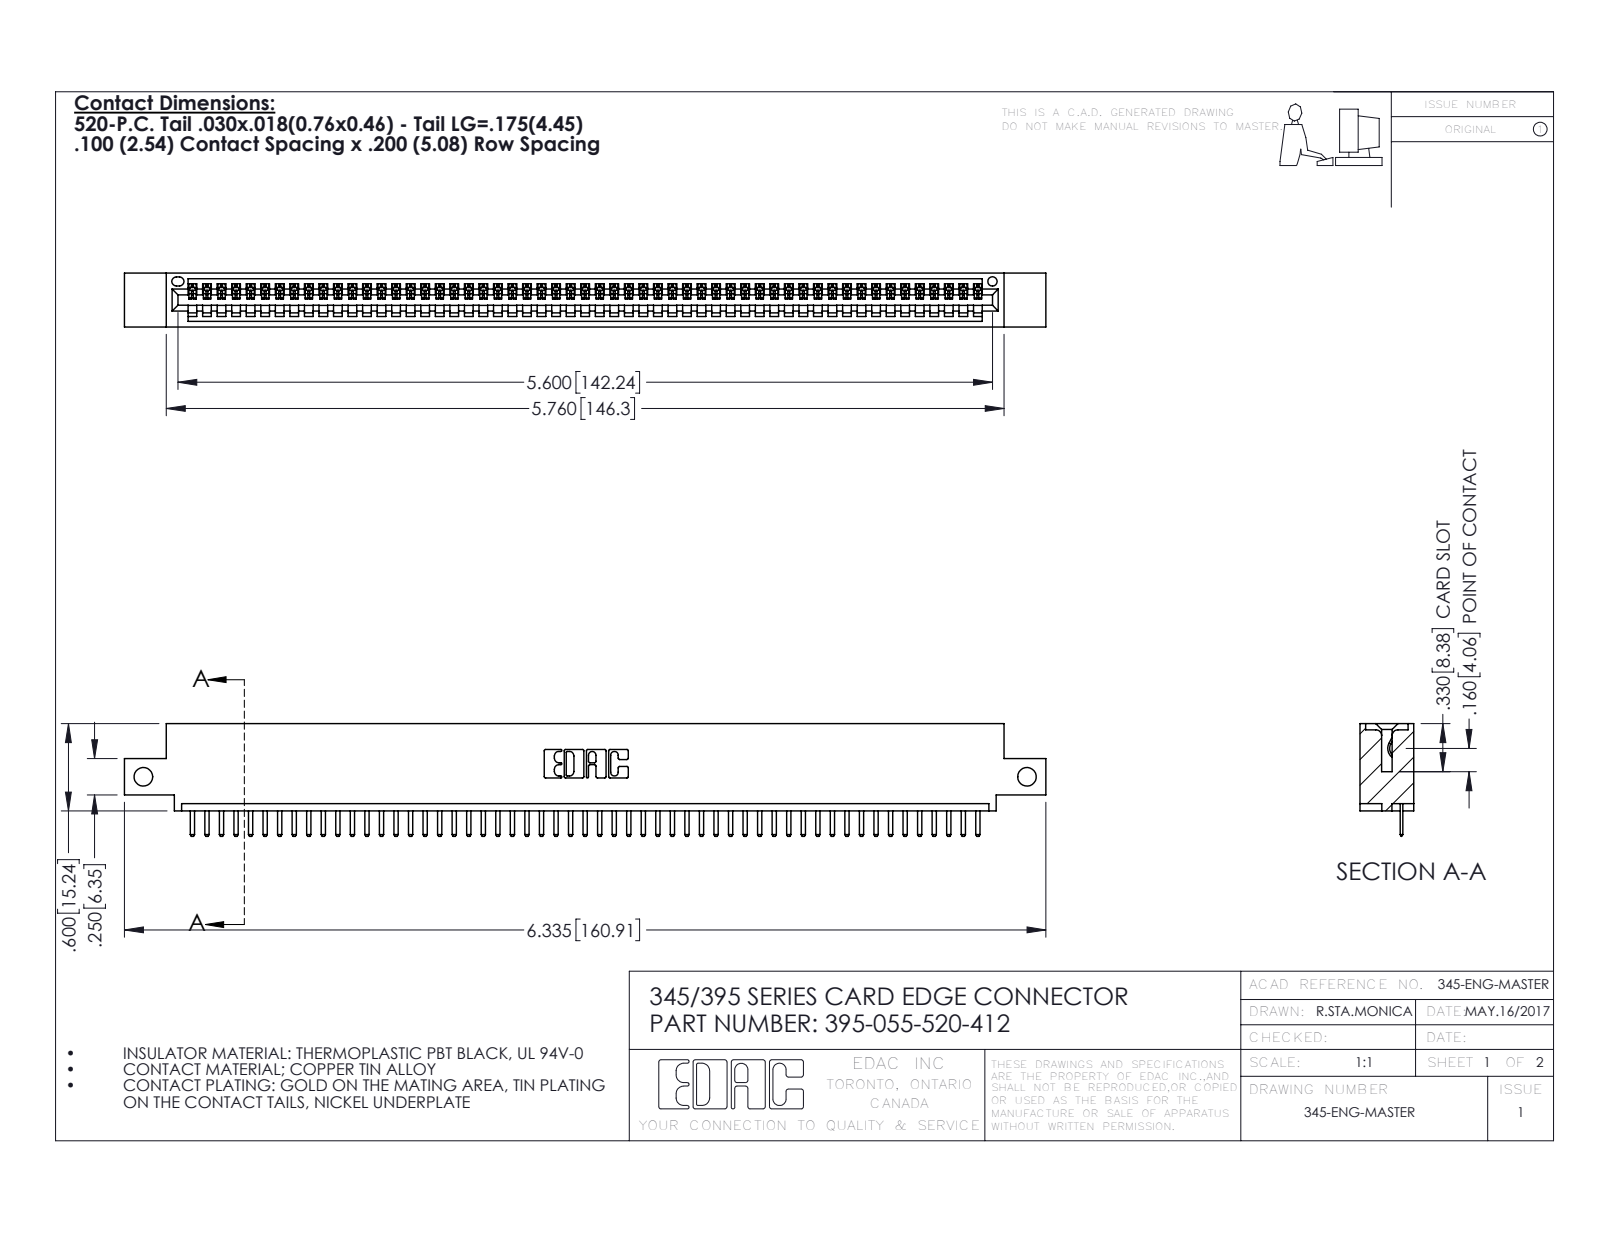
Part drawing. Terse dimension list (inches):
name: 395-055-520-412; 345-292-001_345-293-120; 345 Part_0.110 Offset - Side Mount
written by: SolidWorks 2016 (CONFIG_CONTROL_DESIGN)
unit: in
bodies: 56 solids, 3540 faces (2394 planar, 1146 cylindrical, 0 other)
size: 6.335 × 0.775 × 0.37
volume: 0.92 in³; area: 30.42 in²
holes: 2× ⌀0.128, 1× ⌀0.064
rounds: 112× R0.01, 110× R0.006, 22× R0.01, 6× R0.007, 6× R0.031, 3× R0.026, 2× R0.031, 2× R0.04
face distances: 0.072, 0.298, 0.37, 0.2, 0.098, 0.272, 0.025, 0.225, 0.072, 0.149
hole spacings: 6.075
